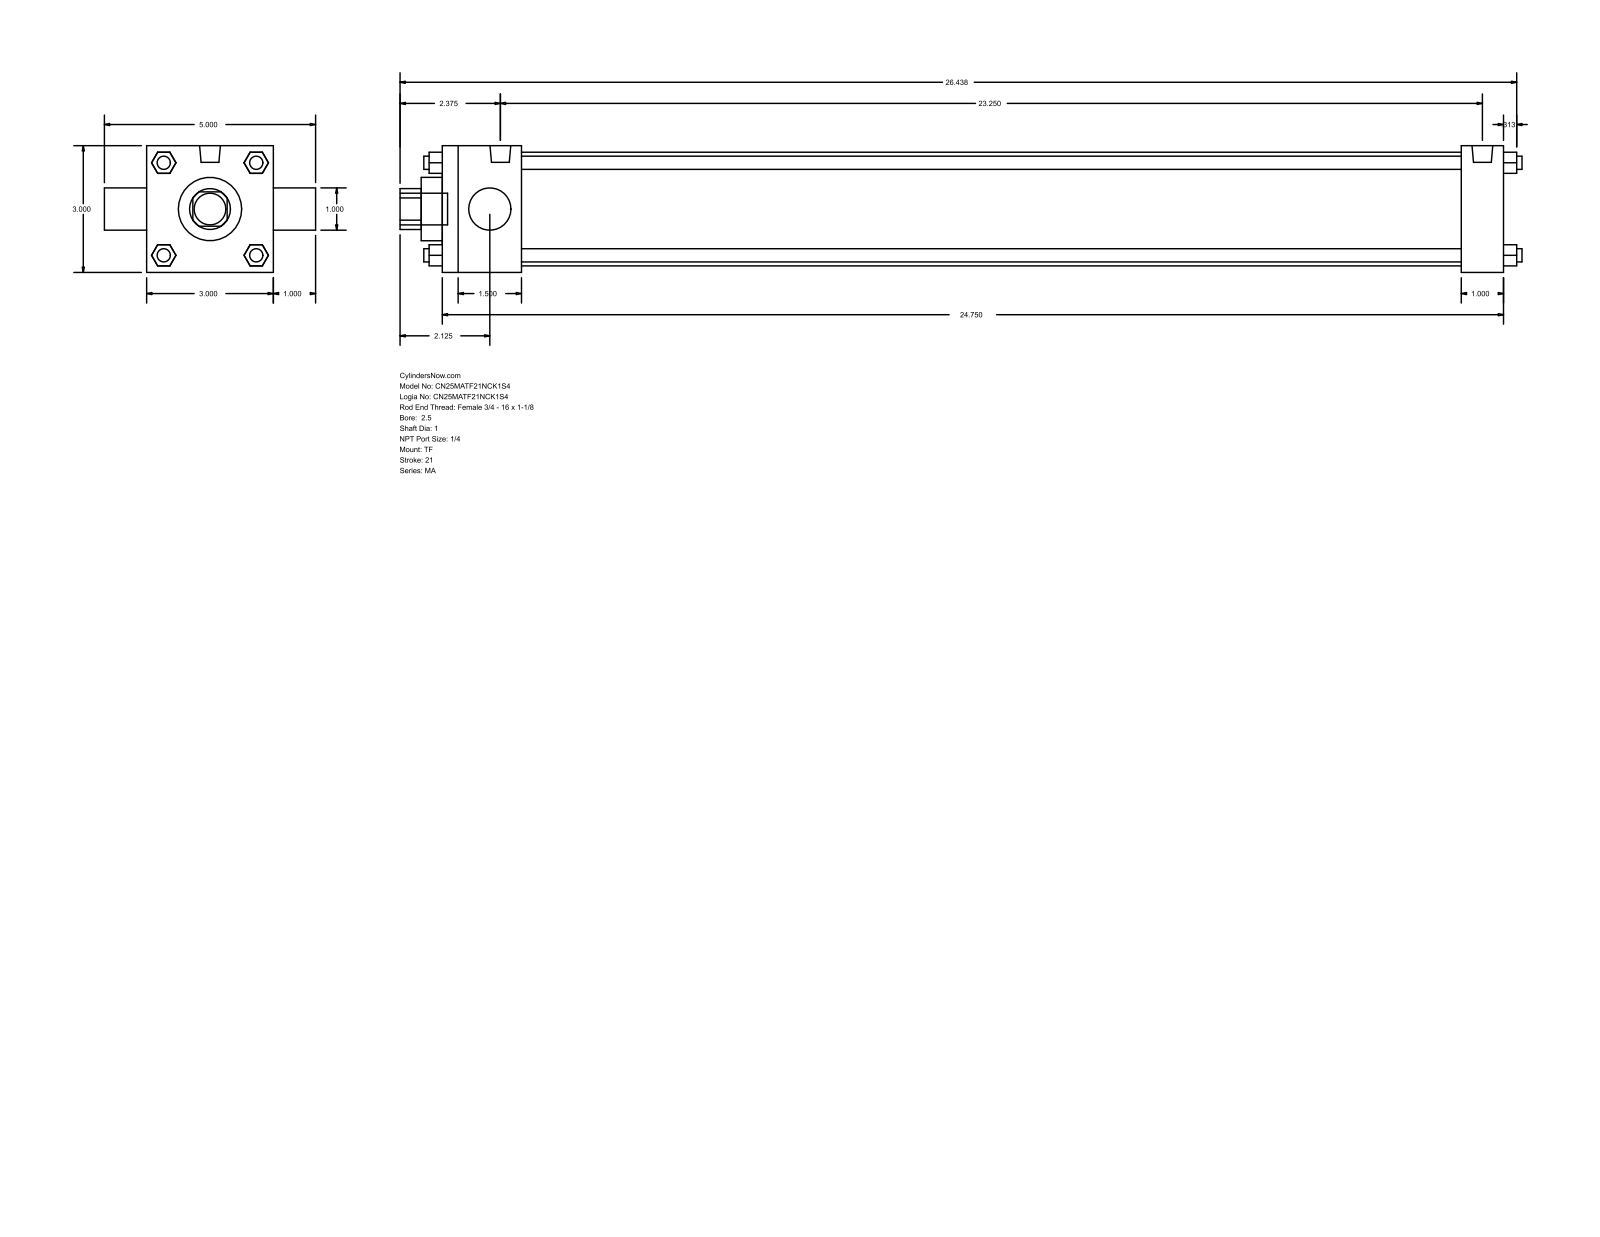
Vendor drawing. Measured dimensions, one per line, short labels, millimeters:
name: MA_TF__0250_1
written by: GSSL Pune (CONFIG_CONTROL_DESIGN)
unit: mm
bodies: 0 solids, 120 faces (92 planar, 28 cylindrical, 0 other)
size: 674.69 × 127 × 76.2
holes: 2× ⌀25.4, 1× ⌀38.1, 1× ⌀68.33
bosses: 7× ⌀7.94, 2× ⌀12.49, 1× ⌀19.05
rounds: 1× R12.29
face distances: 76.2, 638.18, 12.7, 47.63, 612.77, 565.14, 590.55, 25.41, 25.4, 101.6
